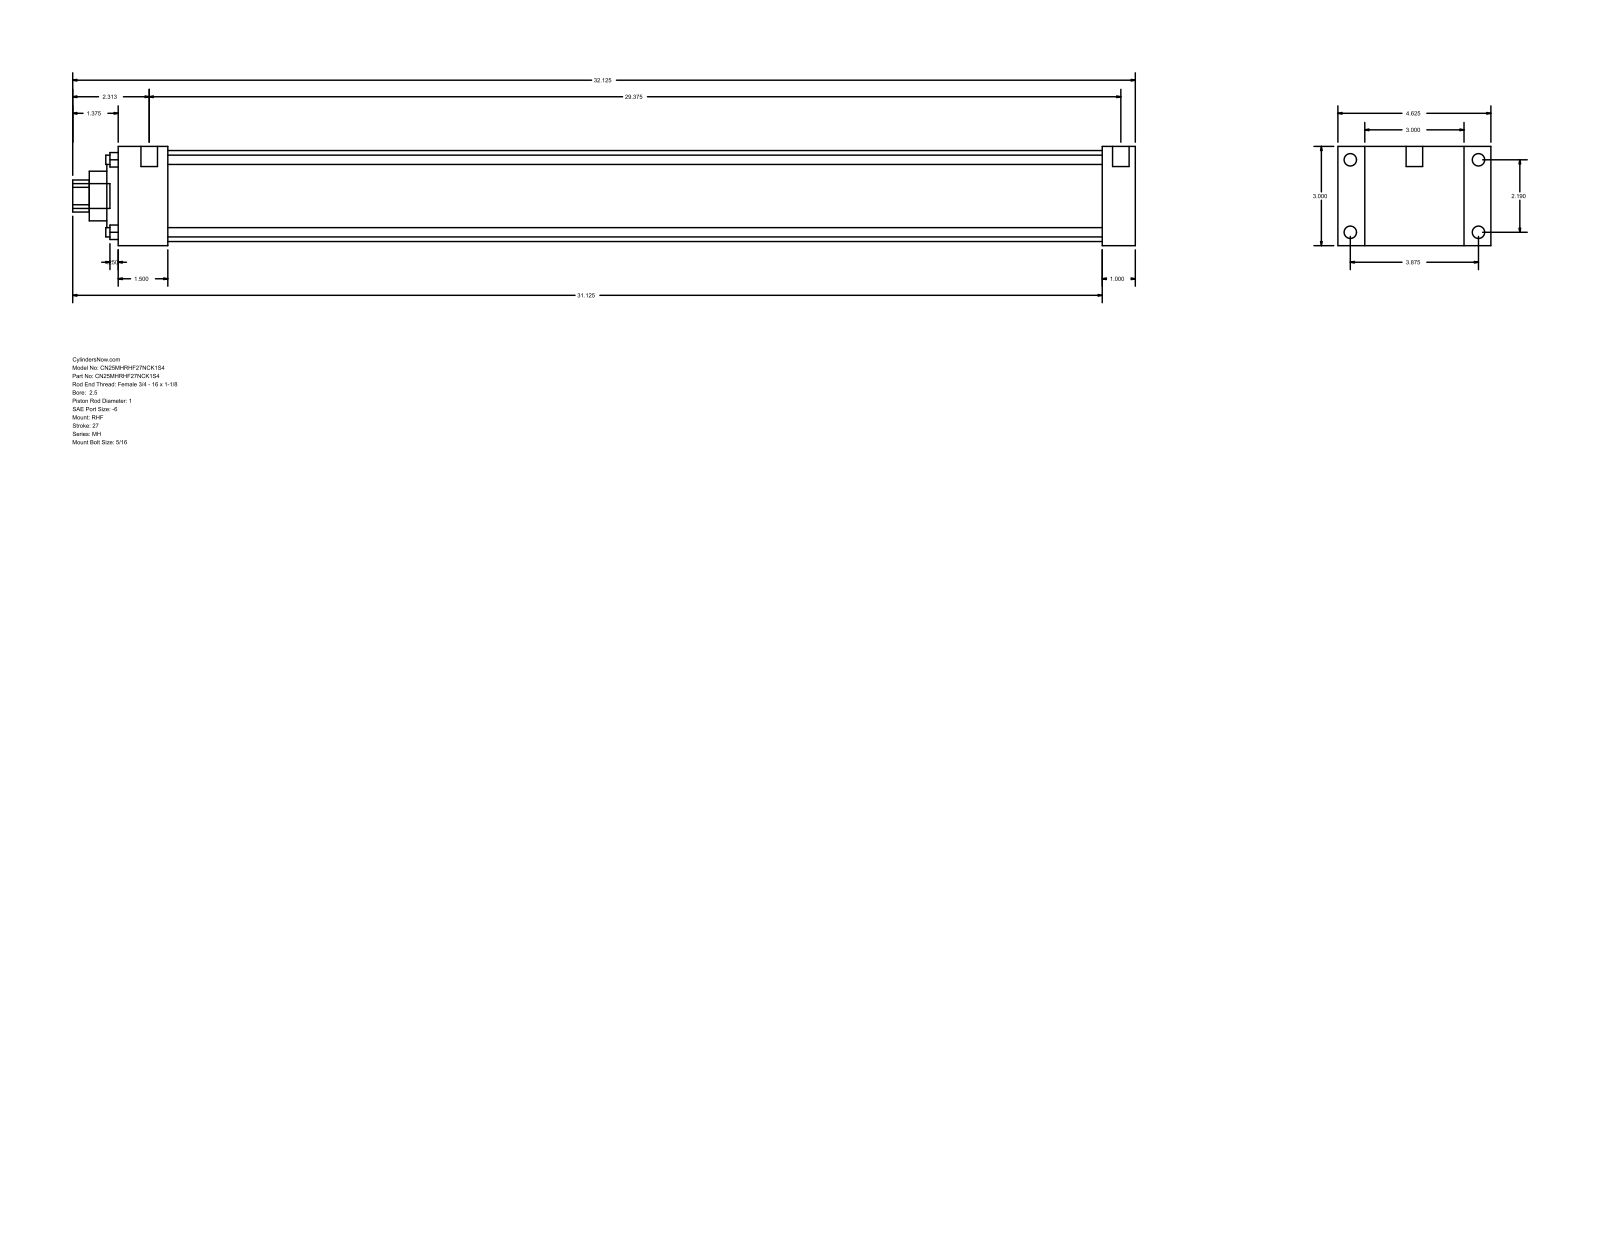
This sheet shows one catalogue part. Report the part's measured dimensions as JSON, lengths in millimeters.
{"part_name": "MH_RHF__0250_1", "step_written_by": "GSSL Pune (CONFIG_CONTROL_DESIGN)", "units": "millimeters", "bodies": {"solids": 0, "faces": 90, "planar": 61, "cylindrical": 29, "other": 0}, "overall_size": [815.98, 117.47, 76.2], "round_holes": [[7.14, 4], [25.4, 1], [38.1, 1], [60.33, 1], [69.85, 1]], "round_bosses_or_shafts": [[9.53, 4], [5.56, 4], [12.7, 2], [19.05, 1]], "partial_cylinders_radius": [[12.29, 1]], "face_to_face_distances": [76.2, 25.4, 20.64, 96.84, 755.66, 781.06, 117.48, 38.11, 717.55, 742.95], "hole_center_spacings": [39.33, 55.62, 78.66]}
